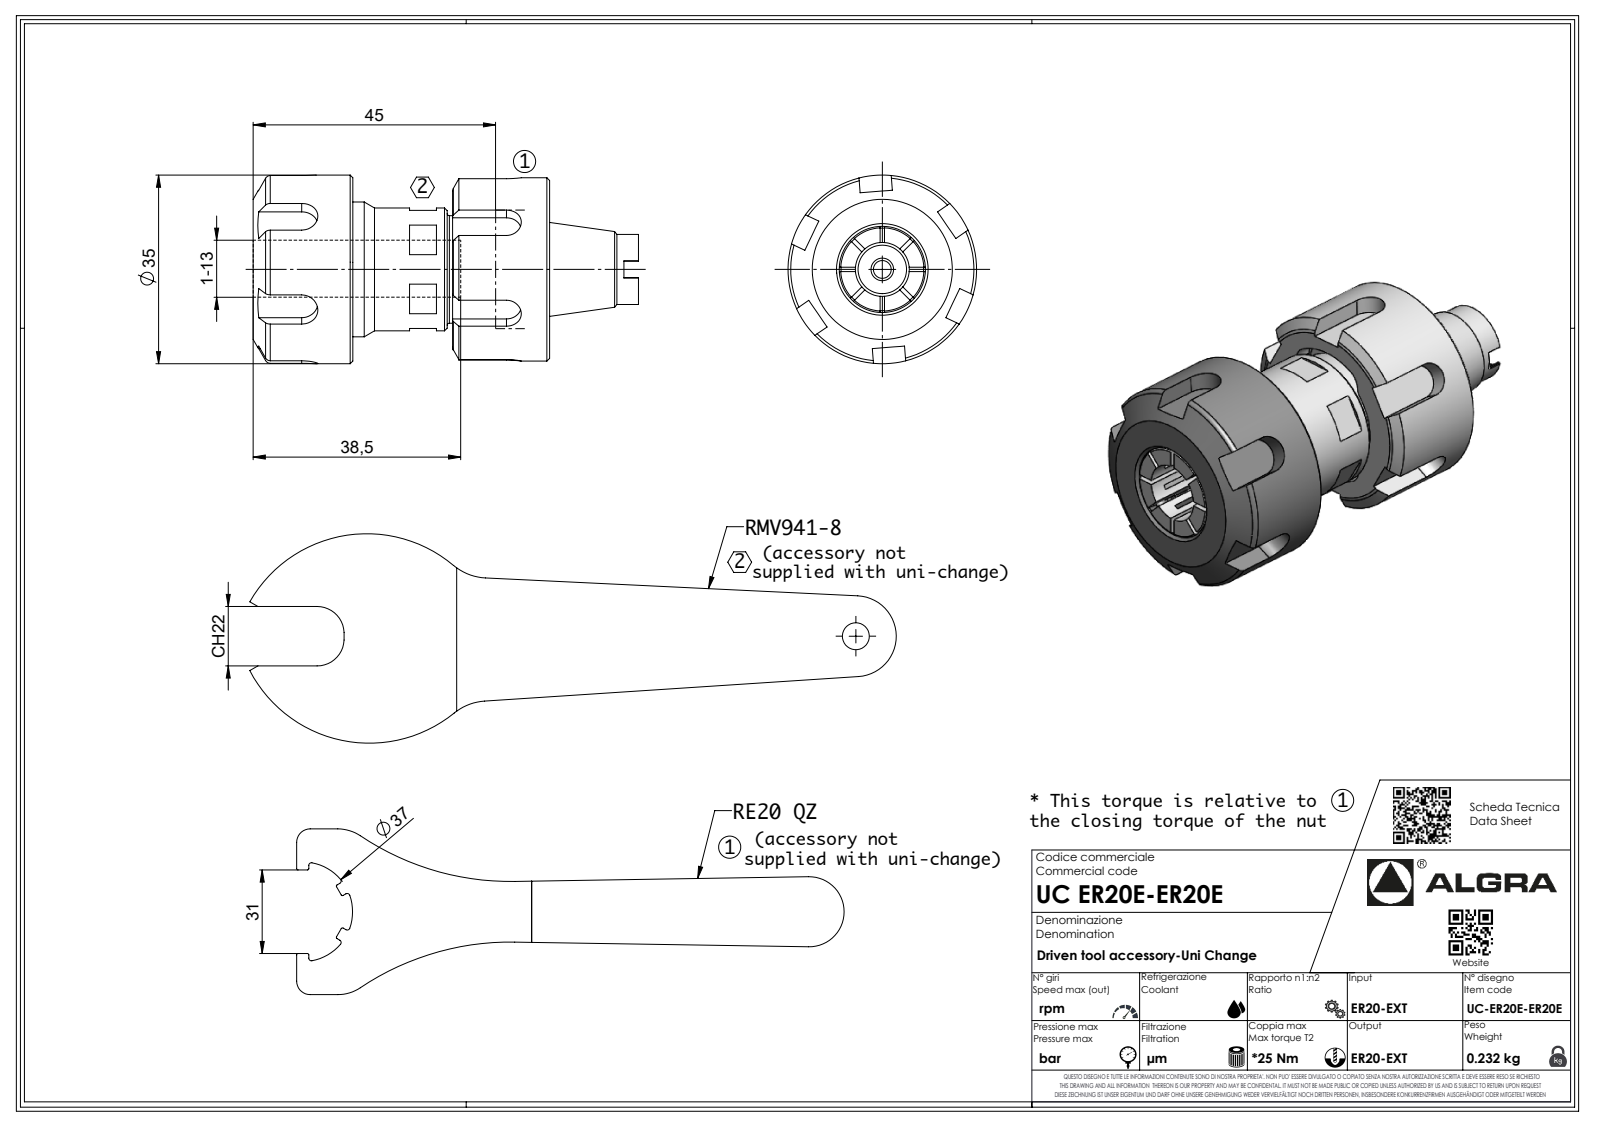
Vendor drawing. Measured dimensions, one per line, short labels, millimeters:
name: UCER20E-ER20E
written by: SolidWorks 2016 (AUTOMOTIVE_DESIGN)
unit: mm
bodies: 1 solid, 413 faces (268 planar, 58 cylindrical, 87 other)
size: 71.52 × 35 × 35
volume: 41 662 mm³; area: 9 475 mm²
holes: 1× ⌀1.57
bosses: 1× ⌀35, 1× ⌀34, 1× ⌀25, 1× ⌀22.8, 1× ⌀19.95, 1× ⌀13, 1× ⌀4.77, 1× ⌀1.27
rounds: 8× R0.1, 7× R0.25, 7× R0.39, 7× R2.78, 5× R3, 4× R2.75, 2× R2.58, 1× R0.16
face distances: 55.02, 36.52, 18.5, 18, 18.52, 37.02, 28, 29, 5.5, 6
